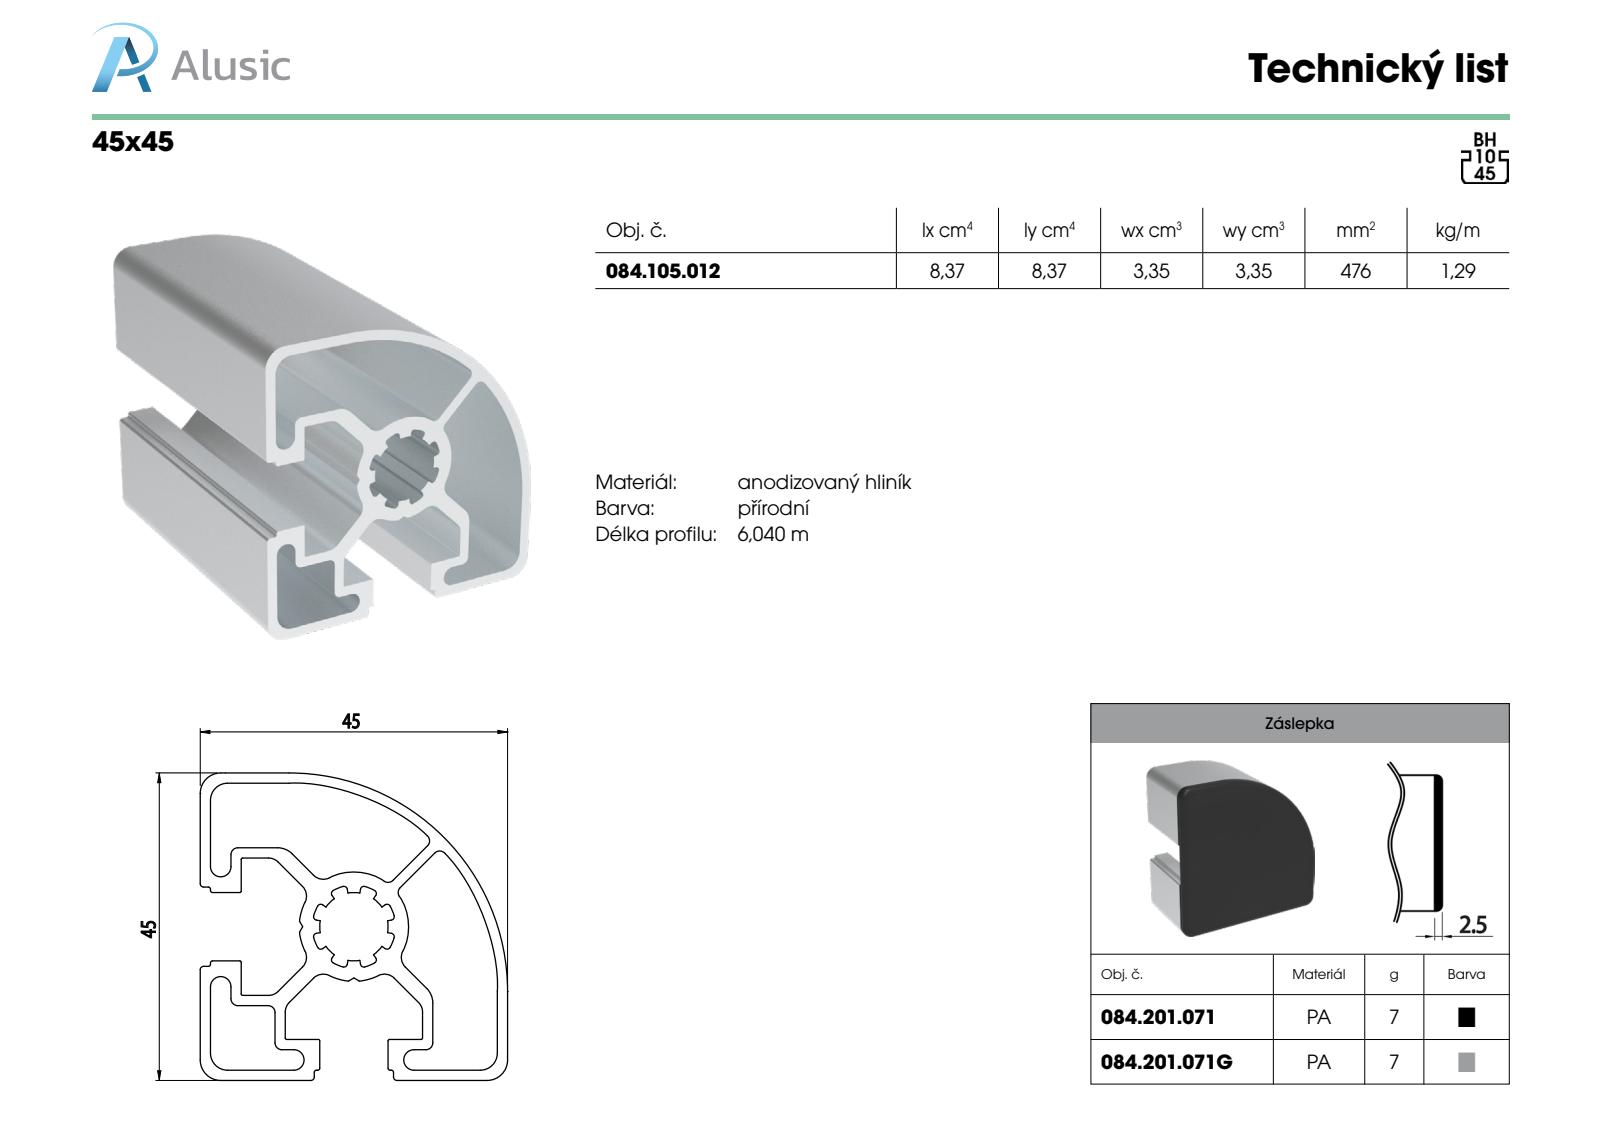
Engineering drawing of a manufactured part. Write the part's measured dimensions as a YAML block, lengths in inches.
part_name: "084.105.012"
step_written_by: "SolidWorks 2018 (AUTOMOTIVE_DESIGN)"
units: inches
bodies: {solids: 1, faces: 172, planar: 70, cylindrical: 102, other: 0}
overall_size: [3.937, 1.772, 1.772]
volume: 2.905
surface_area: 82.68
partial_cylinders:
  - {radius: 0.02, count: 20}
  - {radius: 0.079, count: 10}
  - {radius: 0.039, count: 9}
  - {radius: 0.008, count: 8}
  - {radius: 0.012, count: 8}
  - {radius: 0.118, count: 5}
  - {radius: 0.059, count: 4}
  - {radius: 0.098, count: 3}
face_to_face_distances: [0.059, 1.713, 0.431, 1.281, 0.177, 1.535, 1.341, 0.372, 1.772, 1.104]
